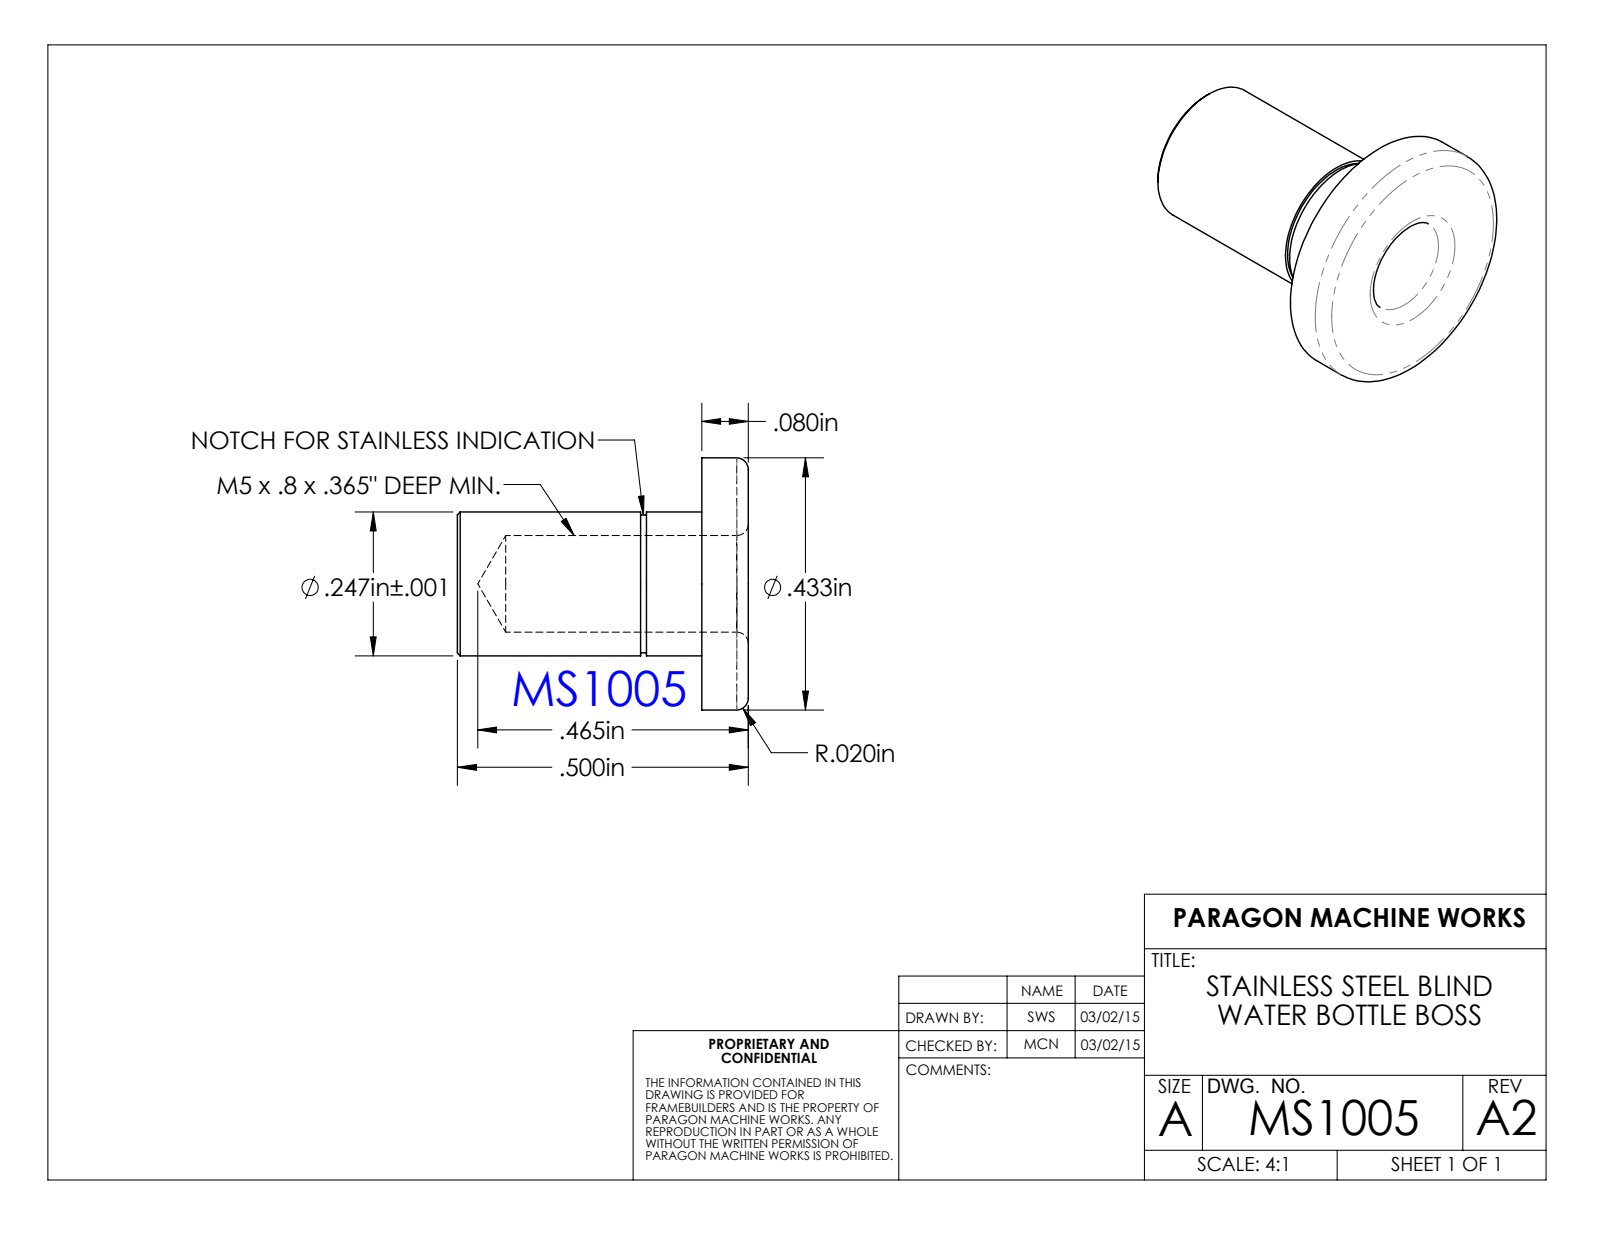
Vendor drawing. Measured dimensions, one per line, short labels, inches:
name: MS1005
written by: SolidWorks 2023 (AUTOMOTIVE_DESIGN)
unit: in
bodies: 1 solid, 23 faces (5 planar, 10 cylindrical, 8 other)
size: 0.5 × 0.433 × 0.433
volume: 0.022 in³; area: 0.939 in²
holes: 1× ⌀0.166
bosses: 1× ⌀0.433, 1× ⌀0.247, 1× ⌀0.237
face distances: 0.08, 0.42, 0.5, 0.315, 0.325, 0.105, 0.185, 0.095, 0.175
